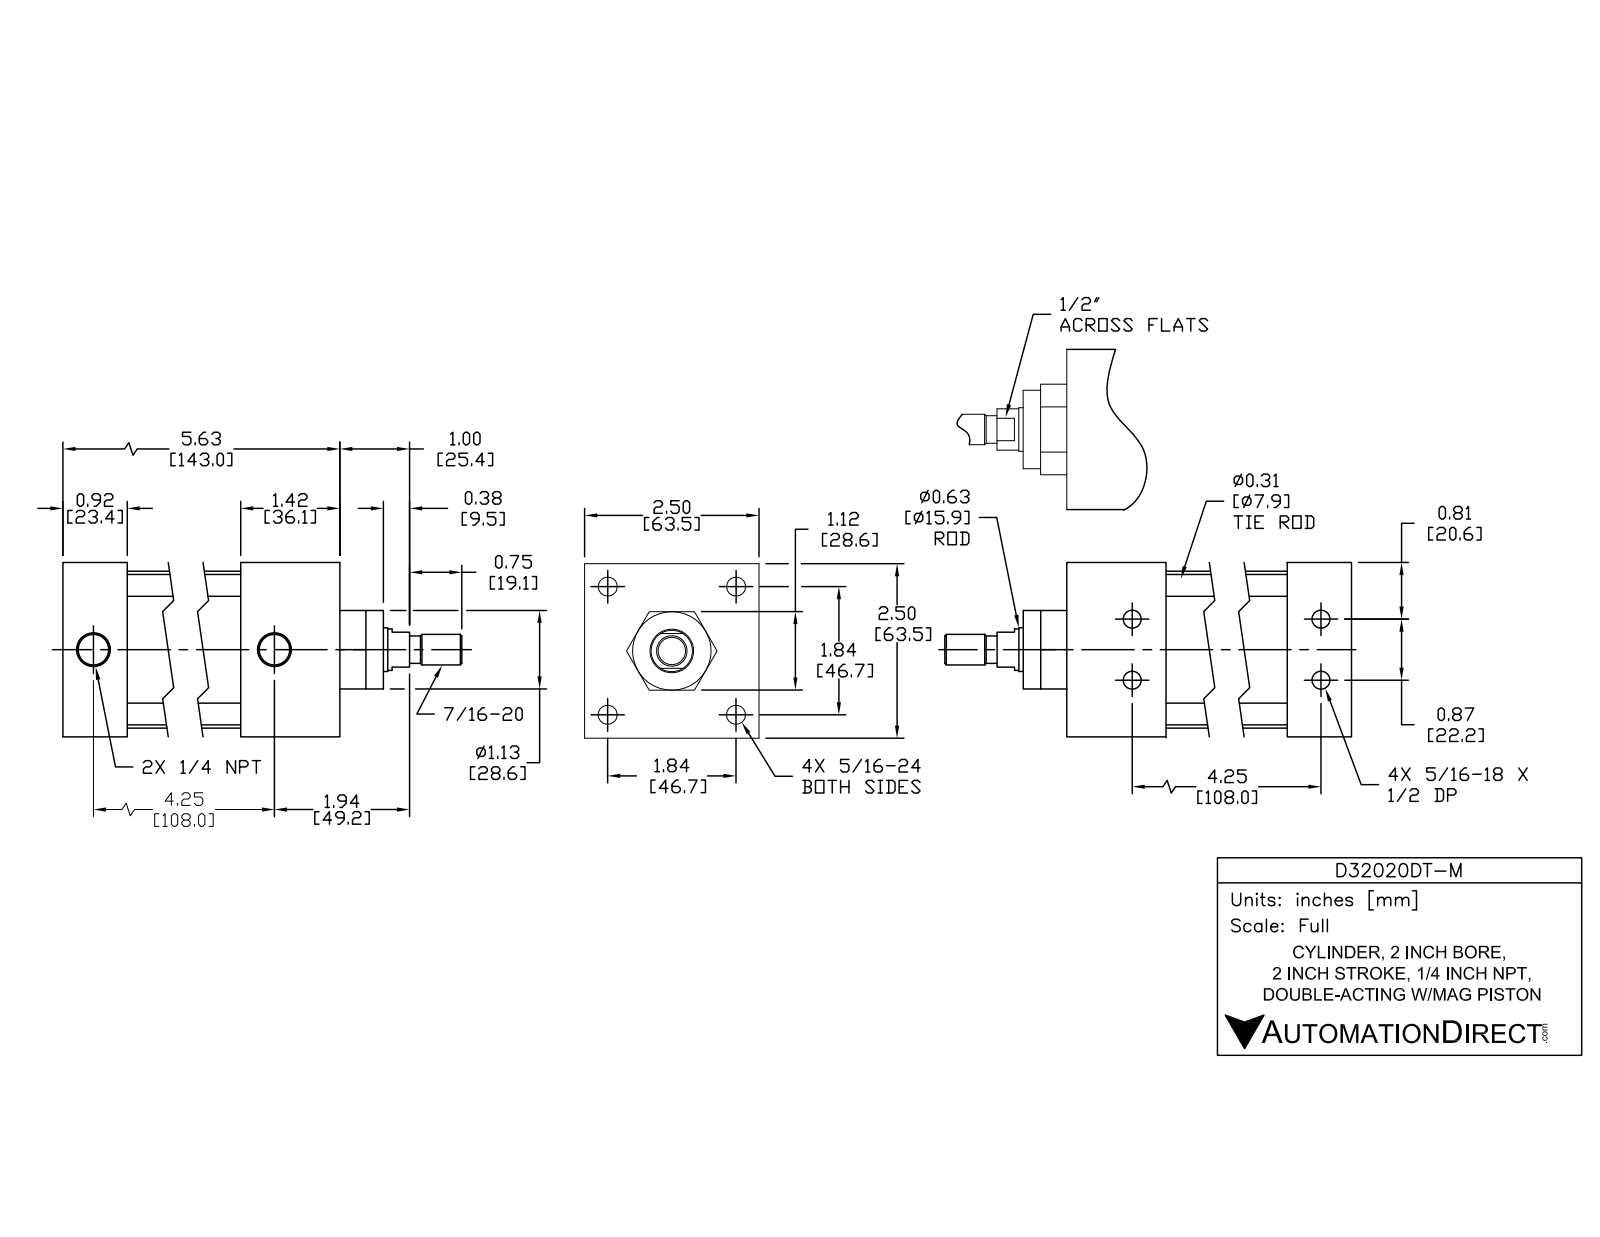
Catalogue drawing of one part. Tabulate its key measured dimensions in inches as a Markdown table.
| quantity | value |
| --- | --- |
| part name | D32020DT-M BODY; D32020DT-M PISTON; D32020DT-M |
| STEP written by | SolidWorks 2015 (AUTOMOTIVE_DESIGN) |
| units | inches |
| bodies | 12 solids, 298 faces (94 planar, 114 cylindrical, 90 other) |
| overall size | 7.371 × 2.5 × 2.5 |
| volume | 22.61 in³ |
| surface area | 161.2 in² |
| round holes (diameter × count) | 0.252 × 4, 0.267 × 4, 0.359 × 4, 0.5 × 4, 0.297 × 2, 0.477 × 2, 0.625 × 1, 0.628 × 1, 2 × 1 |
| round bosses / shafts (diameter × count) | 0.484 × 4, 0.313 × 4, 0.282 × 4, 2.25 × 1, 1.997 × 1, 1.12 × 1, 0.622 × 1, 0.59 × 1 |
| partial cylindrical surfaces (radius × count) | 0.25 × 4 |
| main face-to-face distances | 2.5, 0.08, 3.201, 5.621, 1.42, 4.201, 3.281, 4.701, 0.92, 1 |
| hole center spacings | 4.267, 4.245, 0.437, 0.438, 0.875, 1.306, 1.307, 1.848 |
